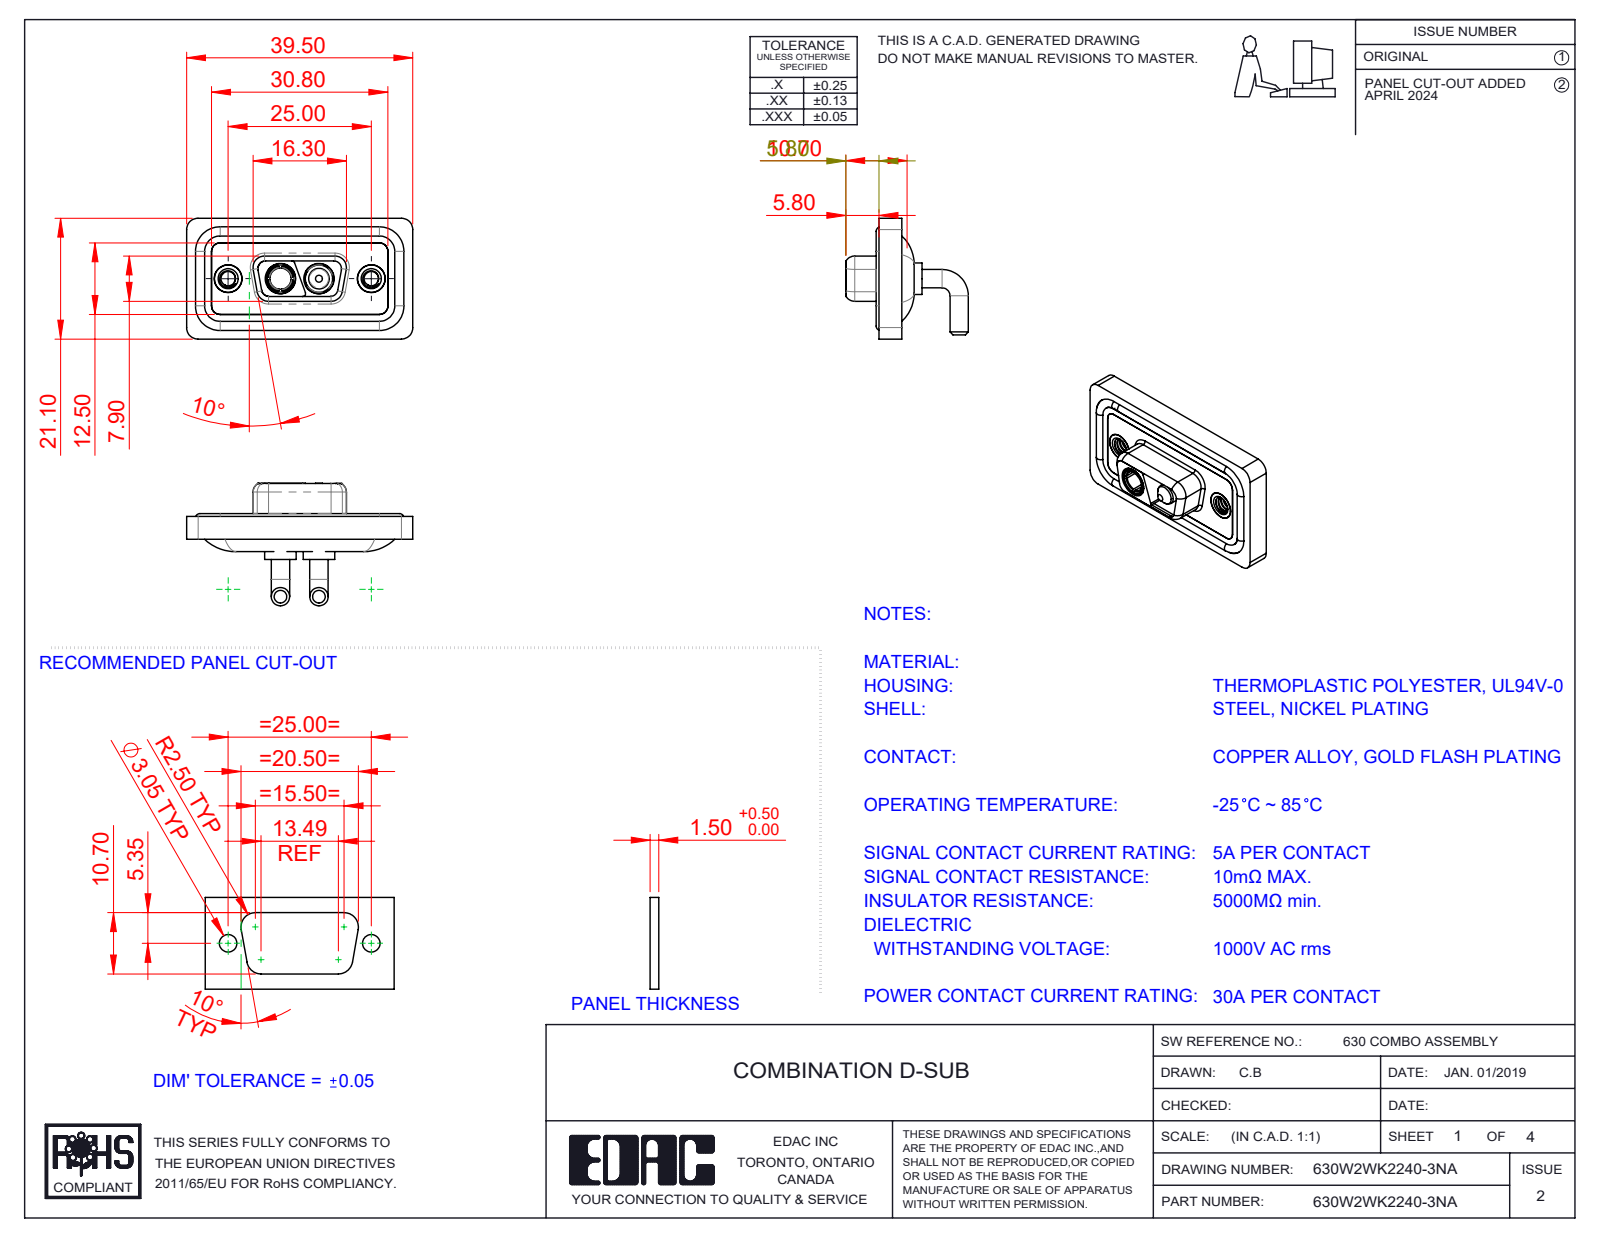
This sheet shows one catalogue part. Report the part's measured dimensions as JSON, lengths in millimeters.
{"part_name": "630Combo Housing_2WK2; Power Pin_30A RA; 630Combo Threaded Rivet_A; 630Combo Waterproof Housing_09 Contacts (+4 more)", "step_written_by": "SolidWorks 2023 (CONFIG_CONTROL_DESIGN)", "units": "millimeters", "bodies": {"solids": 11, "faces": 502, "planar": 144, "cylindrical": 233, "other": 125}, "overall_size": [39.5, 21.4, 21.1], "volume_mm3": 4755, "surface_area_mm2": 7534, "round_holes": [[4.85, 4], [2.5, 2], [4, 2], [4.05, 2], [5, 2], [5.3, 2], [3.7, 1]], "round_bosses_or_shafts": [[3.2, 4], [1.6, 4], [5.5, 2], [5.2, 2], [4.95, 2], [4.8, 2], [4.75, 2], [3.75, 2]], "partial_cylinders_radius": [[1.5, 18], [2, 18], [1.35, 8], [1.6, 8], [0.5, 6], [0.25, 4], [0.6, 4], [0.65, 4]], "face_to_face_distances": [0.4, 1.1, 2.9, 1.8, 2.5, 1.6, 3.1, 1.5, 2.1, 3.7], "hole_center_spacings": [9.14, 15.86, 6.72, 25]}
